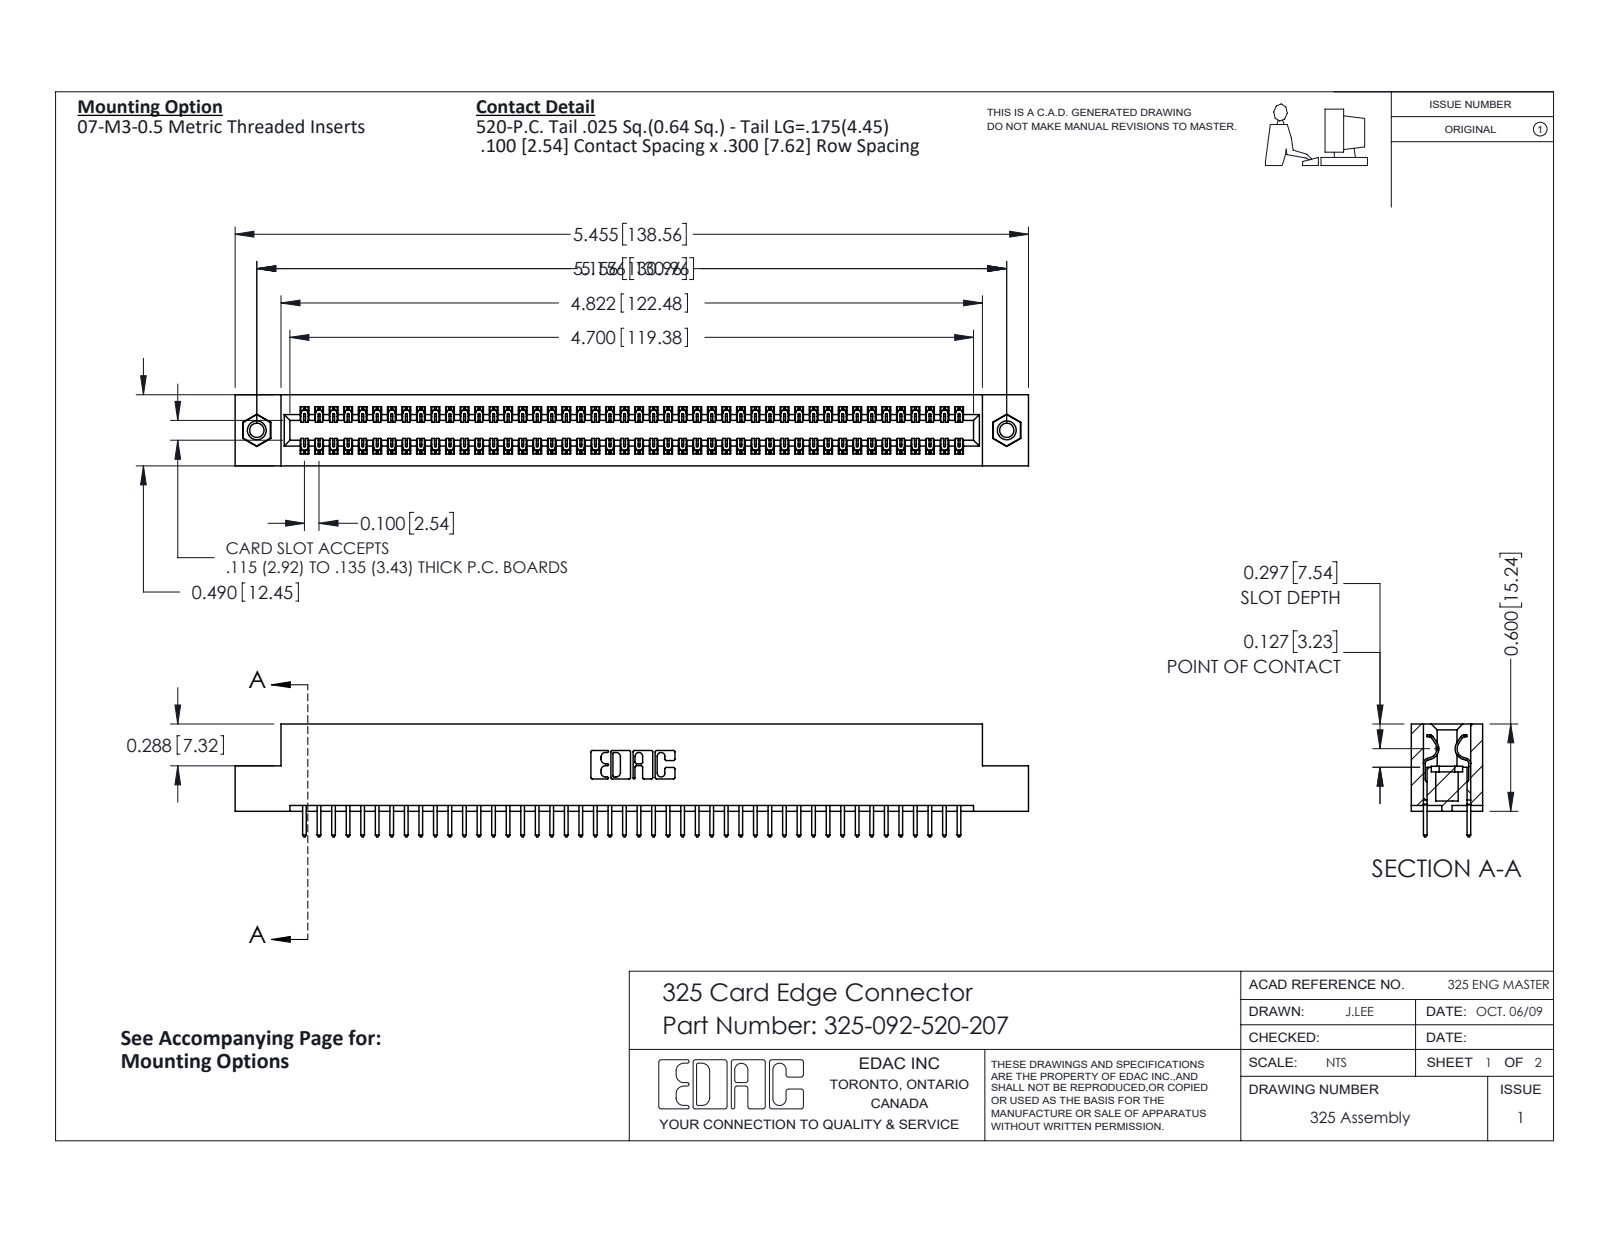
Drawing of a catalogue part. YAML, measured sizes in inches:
part_name: "325 Part_TI; 325-292-001_325-293-120; 345-250-001_345-250-005-103; 325-092-520-207"
step_written_by: "SolidWorks 2016 (CONFIG_CONTROL_DESIGN)"
units: inches
bodies: {solids: 95, faces: 4958, planar: 3414, cylindrical: 1528, other: 16}
overall_size: [5.455, 0.775, 0.49]
volume: 1.092
surface_area: 33.47
round_holes:
  - {diameter: 0.098, count: 2}
  - {diameter: 0.125, count: 2}
  - {diameter: 0.16, count: 2}
round_bosses_or_shafts:
  - {diameter: 0.155, count: 2}
partial_cylinders:
  - {radius: 0.006, count: 138}
  - {radius: 0.01, count: 92}
  - {radius: 0.01, count: 22}
  - {radius: 0.007, count: 6}
  - {radius: 0.031, count: 6}
  - {radius: 0.026, count: 3}
  - {radius: 0.014, count: 2}
  - {radius: 0.022, count: 2}
face_to_face_distances: [0.083, 0.407, 0.3, 0.49, 0.107, 0.383, 0.025, 0.325, 0.275, 0.56]
hole_center_spacings: [5.156]
